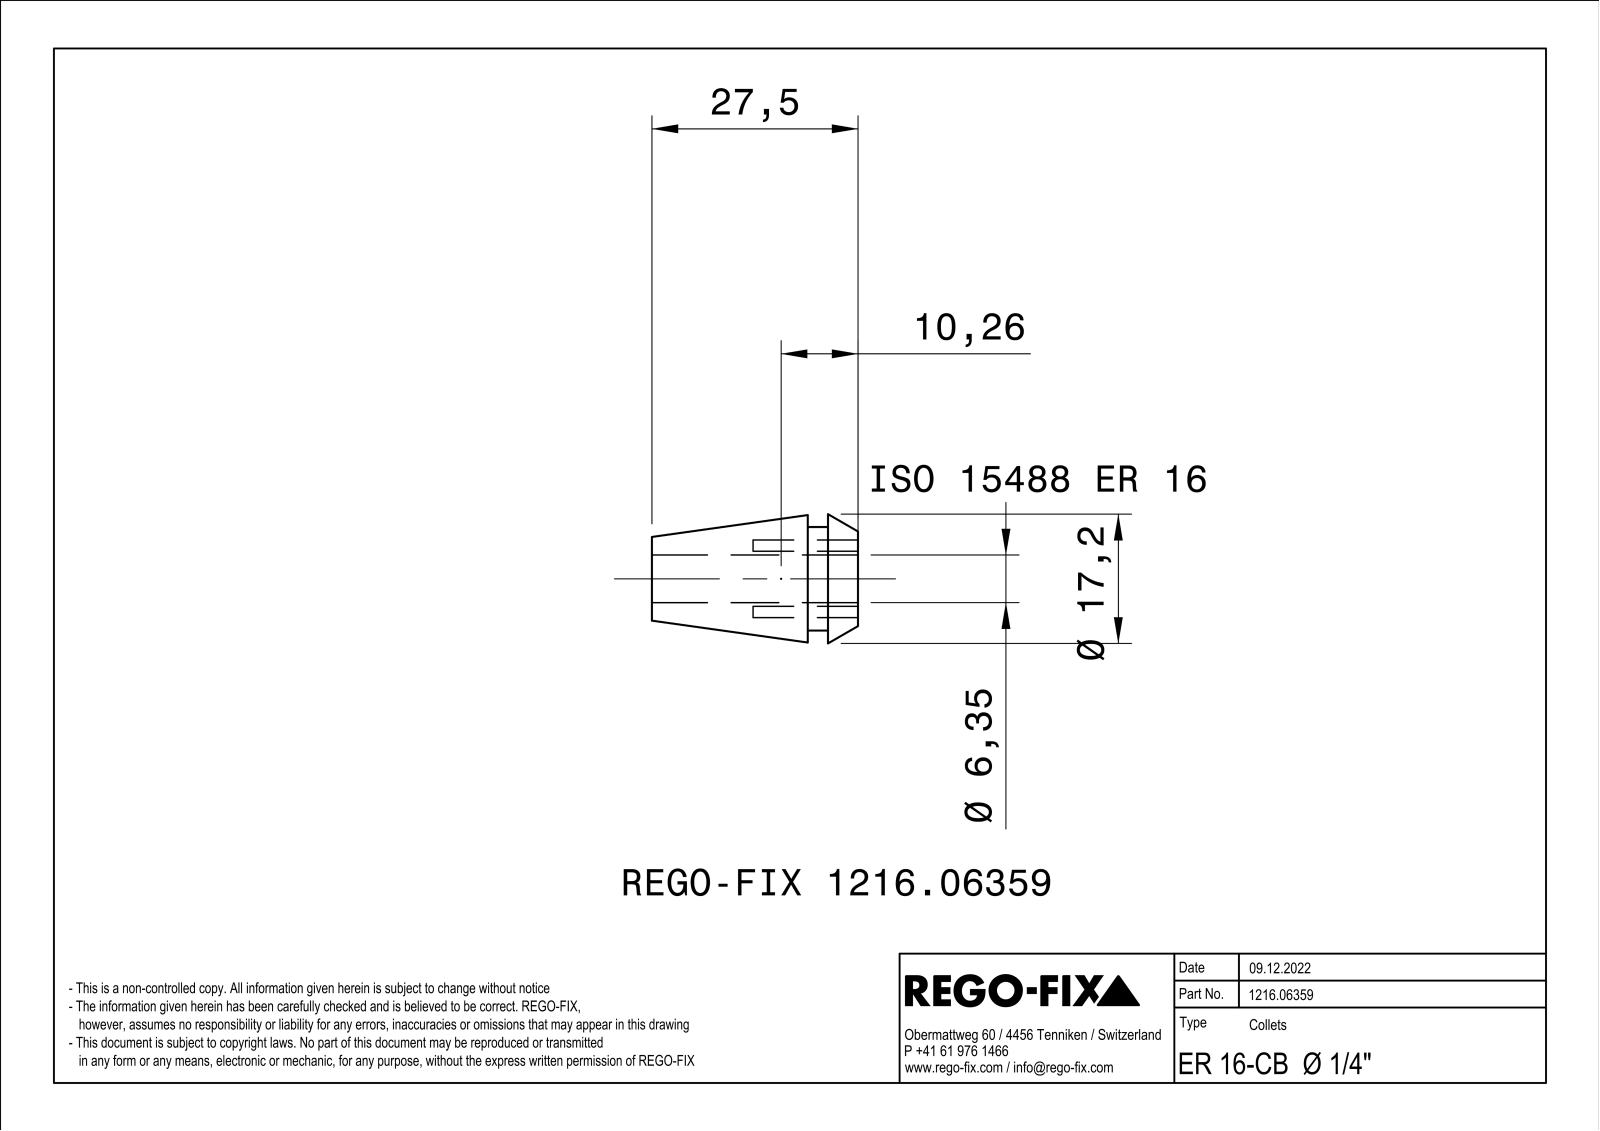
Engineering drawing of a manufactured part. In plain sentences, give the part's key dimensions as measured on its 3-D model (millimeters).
The part is named "NOCUT". Its 3-D file was written by "SIEMENS PLM Software Solid Edge ST10 (AUTOMOTIVE_DESIGN)". It is 1 solid with 178 faces: 64 planar, 21 cylindrical and 93 other. Overall it measures 27.5 by 16.99 by 16.99 millimeters. Its volume is 2 730 cubic millimeters and its surface area 4 269 square millimeters. Round holes: 4 of diameter 1.5, 1 of diameter 6.35. Round bosses or shafts: 1 of diameter 17, 1 of diameter 13.8. The main face-to-face distances are 0.6, 4, 27.5, 23.5, 6.7, 2.7, 20.8. The hole center spacings are 4.43, 6.26, 8.85.
